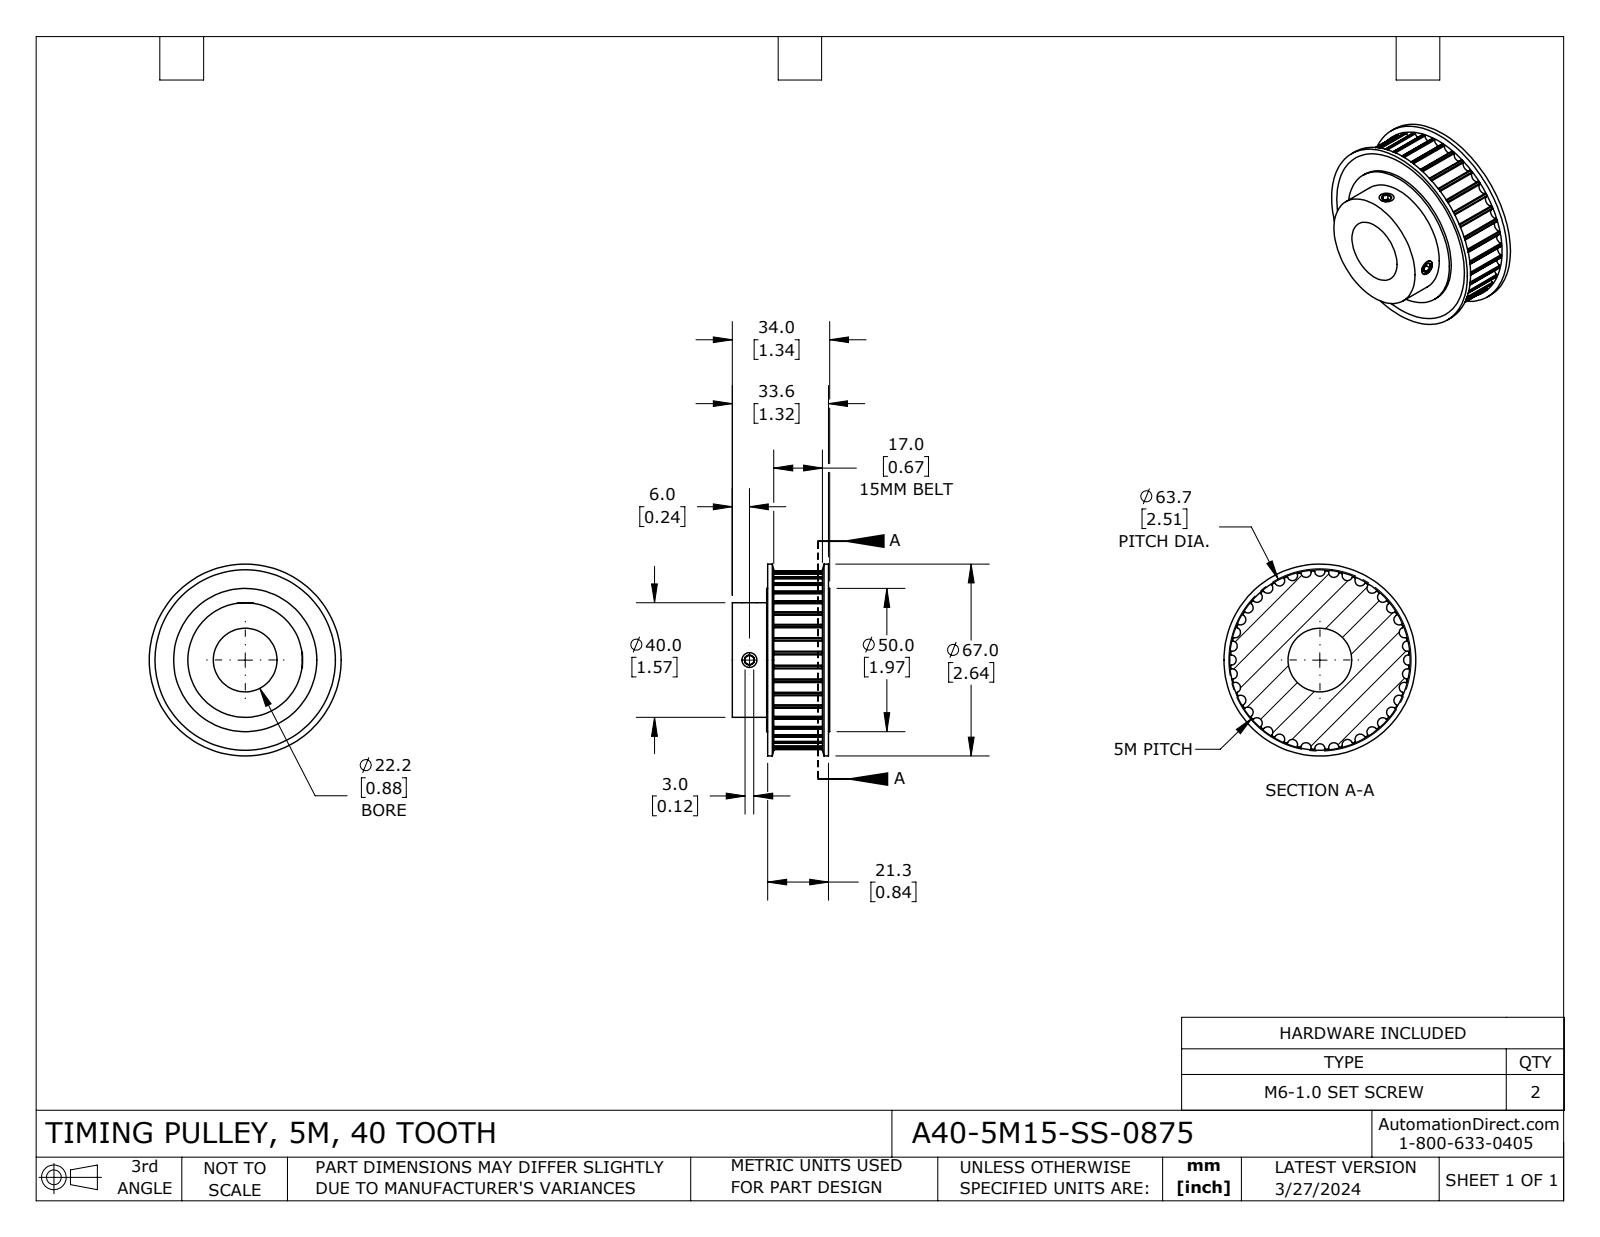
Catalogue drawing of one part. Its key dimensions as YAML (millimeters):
part_name: "A40-5M15-SS-0875"
step_written_by: "SolidWorks 2021 (CONFIG_CONTROL_DESIGN)"
units: millimeters
bodies: {solids: 5, faces: 282, planar: 25, cylindrical: 223, other: 34}
overall_size: [67, 67, 34]
volume: 64754
surface_area: 22310
round_holes:
  - {diameter: 5, count: 2}
  - {diameter: 22.23, count: 1}
  - {diameter: 50, count: 1}
round_bosses_or_shafts:
  - {diameter: 6, count: 2}
  - {diameter: 67, count: 1}
  - {diameter: 40, count: 1}
partial_cylinders:
  - {radius: 0.3, count: 80}
  - {radius: 1.82, count: 40}
  - {radius: 31.26, count: 1}
face_to_face_distances: [1.6, 18.6, 2.5, 19.5, 17, 0.9, 21.1, 20.2, 34, 33.1]
